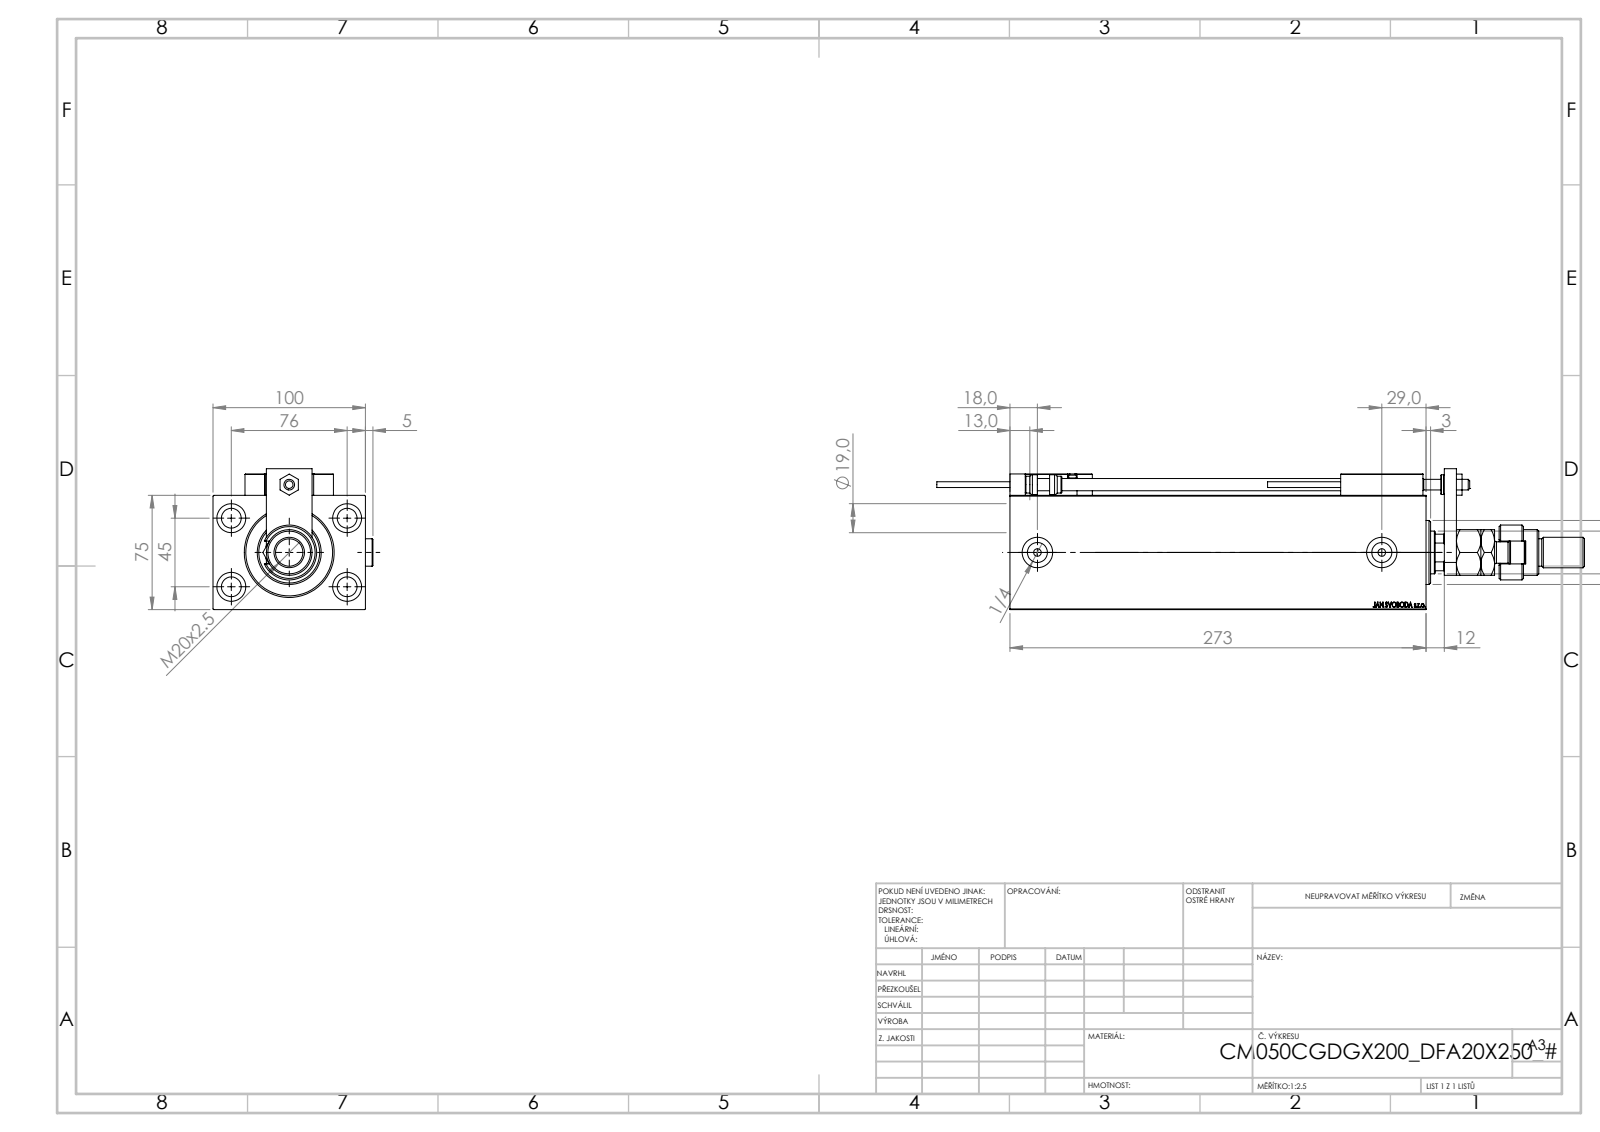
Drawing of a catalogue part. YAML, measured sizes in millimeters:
part_name: "NUT_D12; SWITCH X; V450CM_VC_B; SWITCH_X_FRONT_BACK (+7 more)"
step_written_by: "SolidWorks 2019 (CONFIG_CONTROL_DESIGN)"
units: millimeters
bodies: {solids: 27, faces: 1424, planar: 623, cylindrical: 219, other: 582}
overall_size: [425, 104.9, 92.5]
volume: 1726000
surface_area: 285387
round_holes:
  - {diameter: 8, count: 5}
  - {diameter: 3.2, count: 4}
  - {diameter: 4, count: 4}
  - {diameter: 5, count: 4}
  - {diameter: 13, count: 4}
  - {diameter: 19, count: 4}
  - {diameter: 20, count: 3}
  - {diameter: 13.16, count: 2}
  - {diameter: 7, count: 1}
  - {diameter: 18.5, count: 1}
  - {diameter: 28, count: 1}
  - {diameter: 31.5, count: 1}
round_bosses_or_shafts:
  - {diameter: 18, count: 3}
  - {diameter: 5, count: 2}
  - {diameter: 3.8, count: 2}
  - {diameter: 42, count: 1}
  - {diameter: 36, count: 1}
  - {diameter: 30, count: 1}
  - {diameter: 22, count: 1}
  - {diameter: 14, count: 1}
partial_cylinders:
  - {radius: 0.3, count: 30}
  - {radius: 3, count: 2}
  - {radius: 7.5, count: 1}
  - {radius: 12, count: 1}
  - {radius: 13.5, count: 1}
face_to_face_distances: [75, 100, 14, 273, 12, 259, 20, 8, 24, 25]
hole_center_spacings: [44.16, 11.37, 20, 29.59, 29.69, 36.06, 42.19, 43.91]
